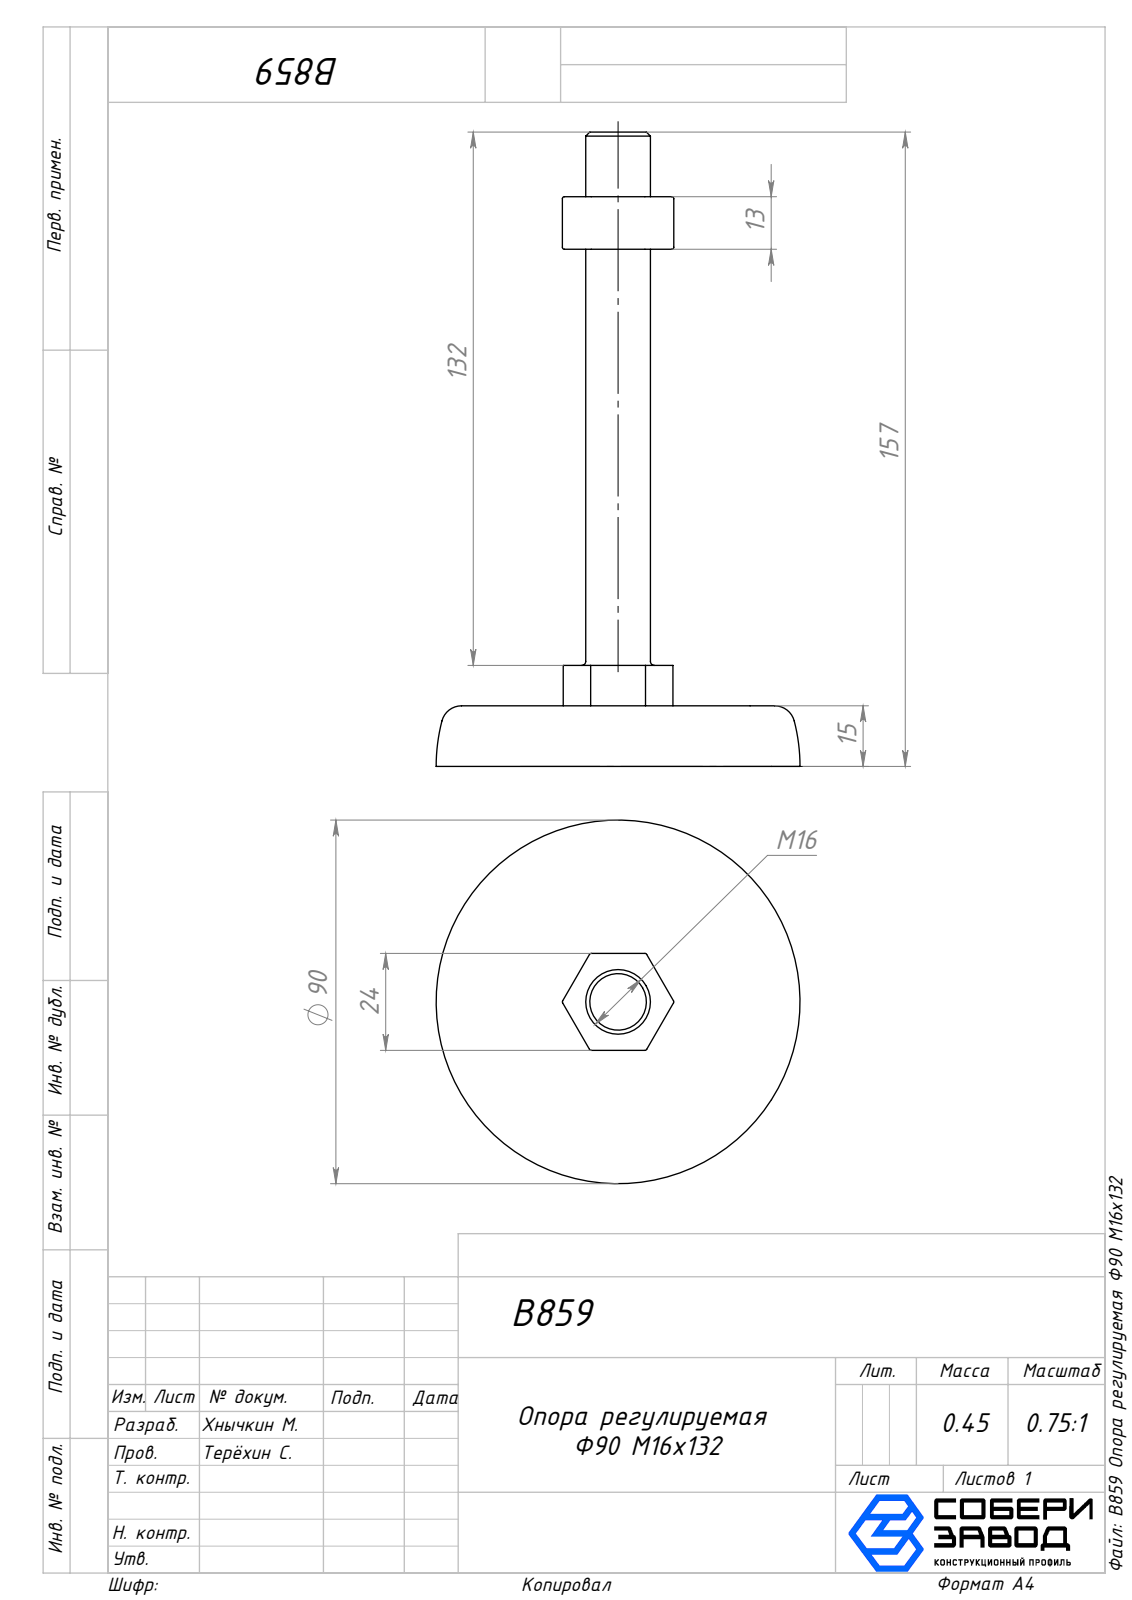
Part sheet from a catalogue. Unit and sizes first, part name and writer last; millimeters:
Units: millimetres
Overall size (bounding box): 157 × 90 × 90
Round holes (diameter × count): ⌀4 ×1, ⌀5 ×1, ⌀14 ×1
Round bosses / shafts (diameter × count): ⌀16 ×1
Partial cylindrical surfaces — rounded edges, fillets, slot ends (radius × count): R0.5 ×36
Main face-to-face distances: 14.8, 15, 23.75, 24, 23.5, 10, 141, 126.2, 126, 128
Volume: 52 679 mm³ · Surface area: 30 158 mm²
Bodies: 4 solids, 120 faces (29 planar, 46 cylindrical, 45 other)
Part name (STEP PRODUCT): Мал. гайка_00; B859 Опора регулируемая Ф90 М16х132; Гайка_00; Опора_00 (+1 more)
STEP written by: SolidWorks 2025 (AUTOMOTIVE_DESIGN)
